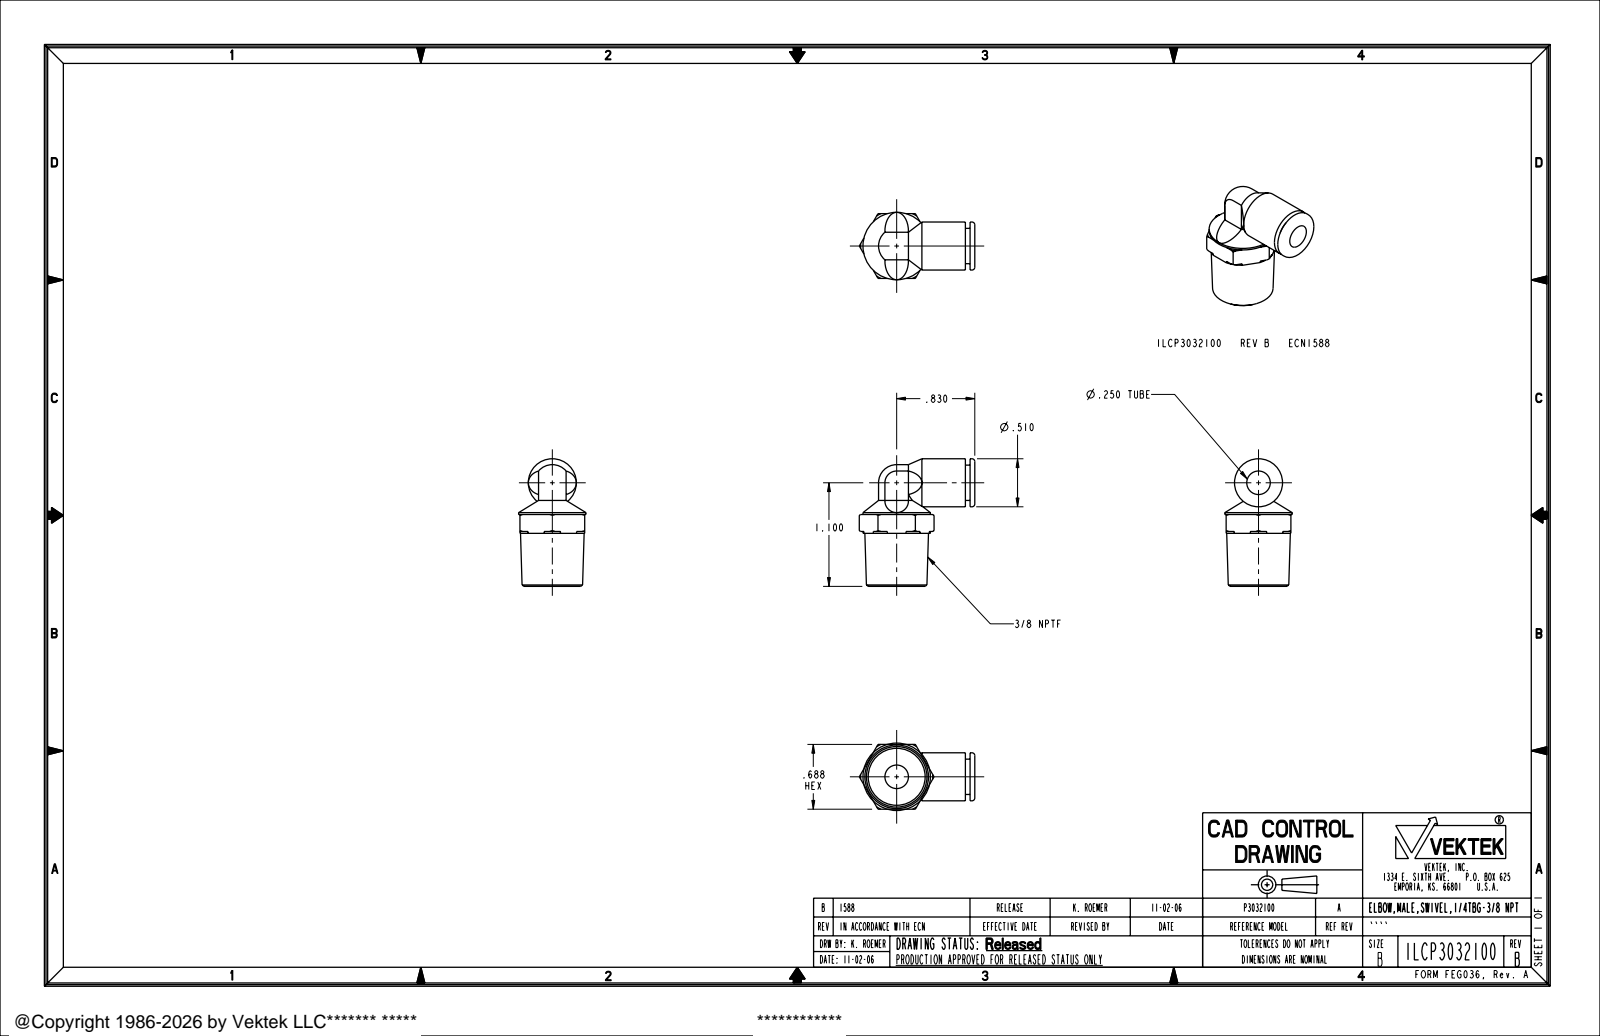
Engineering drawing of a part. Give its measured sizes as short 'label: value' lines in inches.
name: ILCP3032100
written by: PRO/ENGINEER BY PARAMETRIC TECHNOLOGY CORPORATION, 2005180 (AUTOMOTIVE_DESIGN_CC2)
unit: in
bodies: 1 solid, 83 faces (35 planar, 22 cylindrical, 26 other)
size: 1.355 × 1.227 × 0.716
volume: 0.379 in³; area: 5.621 in²
holes: 2× ⌀0.25
bosses: 1× ⌀0.716, 1× ⌀0.51, 1× ⌀0.375
rounds: 2× R0.192
face distances: 0.688, 0.05, 0.198, 0.491, 0.1, 0.293, 0.563, 0.763, 0.2, 0.583
